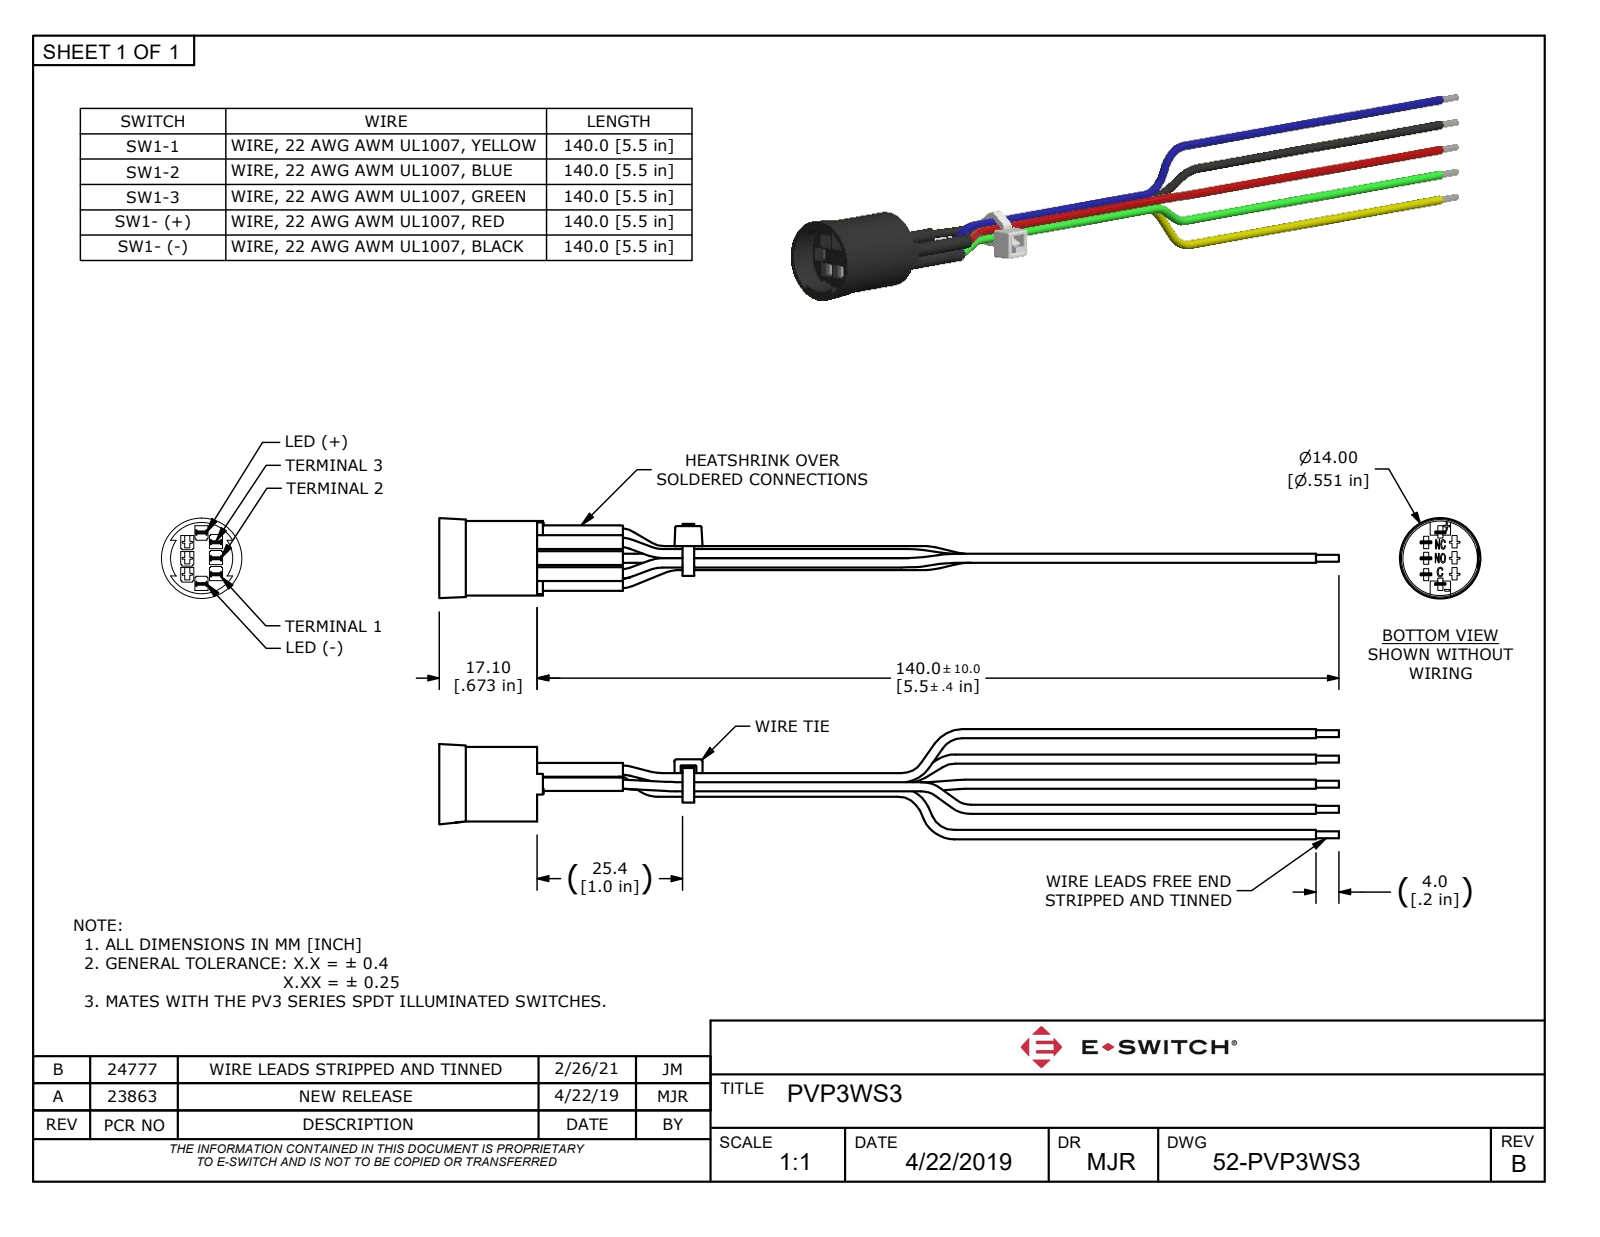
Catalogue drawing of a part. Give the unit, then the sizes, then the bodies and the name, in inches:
Units: inches
Overall size (bounding box): 6.185 × 0.756 × 0.551
Round holes (diameter × count): ⌀0.063 ×7
Round bosses / shafts (diameter × count): ⌀0.063 ×18, ⌀0.047 ×10, ⌀0.094 ×5, ⌀0.512 ×1
Partial cylindrical surfaces — rounded edges, fillets, slot ends (radius × count): R0.01 ×18, R0.008 ×14, R0.043 ×4, R0.035 ×2, R0.246 ×2, R0.213 ×1
Main face-to-face distances: 0.11, 0.098, 0.051, 0.161, 0.059, 0.039, 0.063, 0.091, 0.22, 0.287
Hole centre spacings: 0.11, 0.119, 0.126, 0.127, 0.13, 0.199, 0.203, 0.23
Volume: 0.197 in³ · Surface area: 9.57 in²
Bodies: 1 solid, 566 faces (362 planar, 98 cylindrical, 106 other)
Part name (STEP PRODUCT): PVP3WS3
STEP written by: Autodesk Inventor 2018 (AP242_MANAGED_MODEL_BASED_3D_ENGINEERING_MIM_LF)
